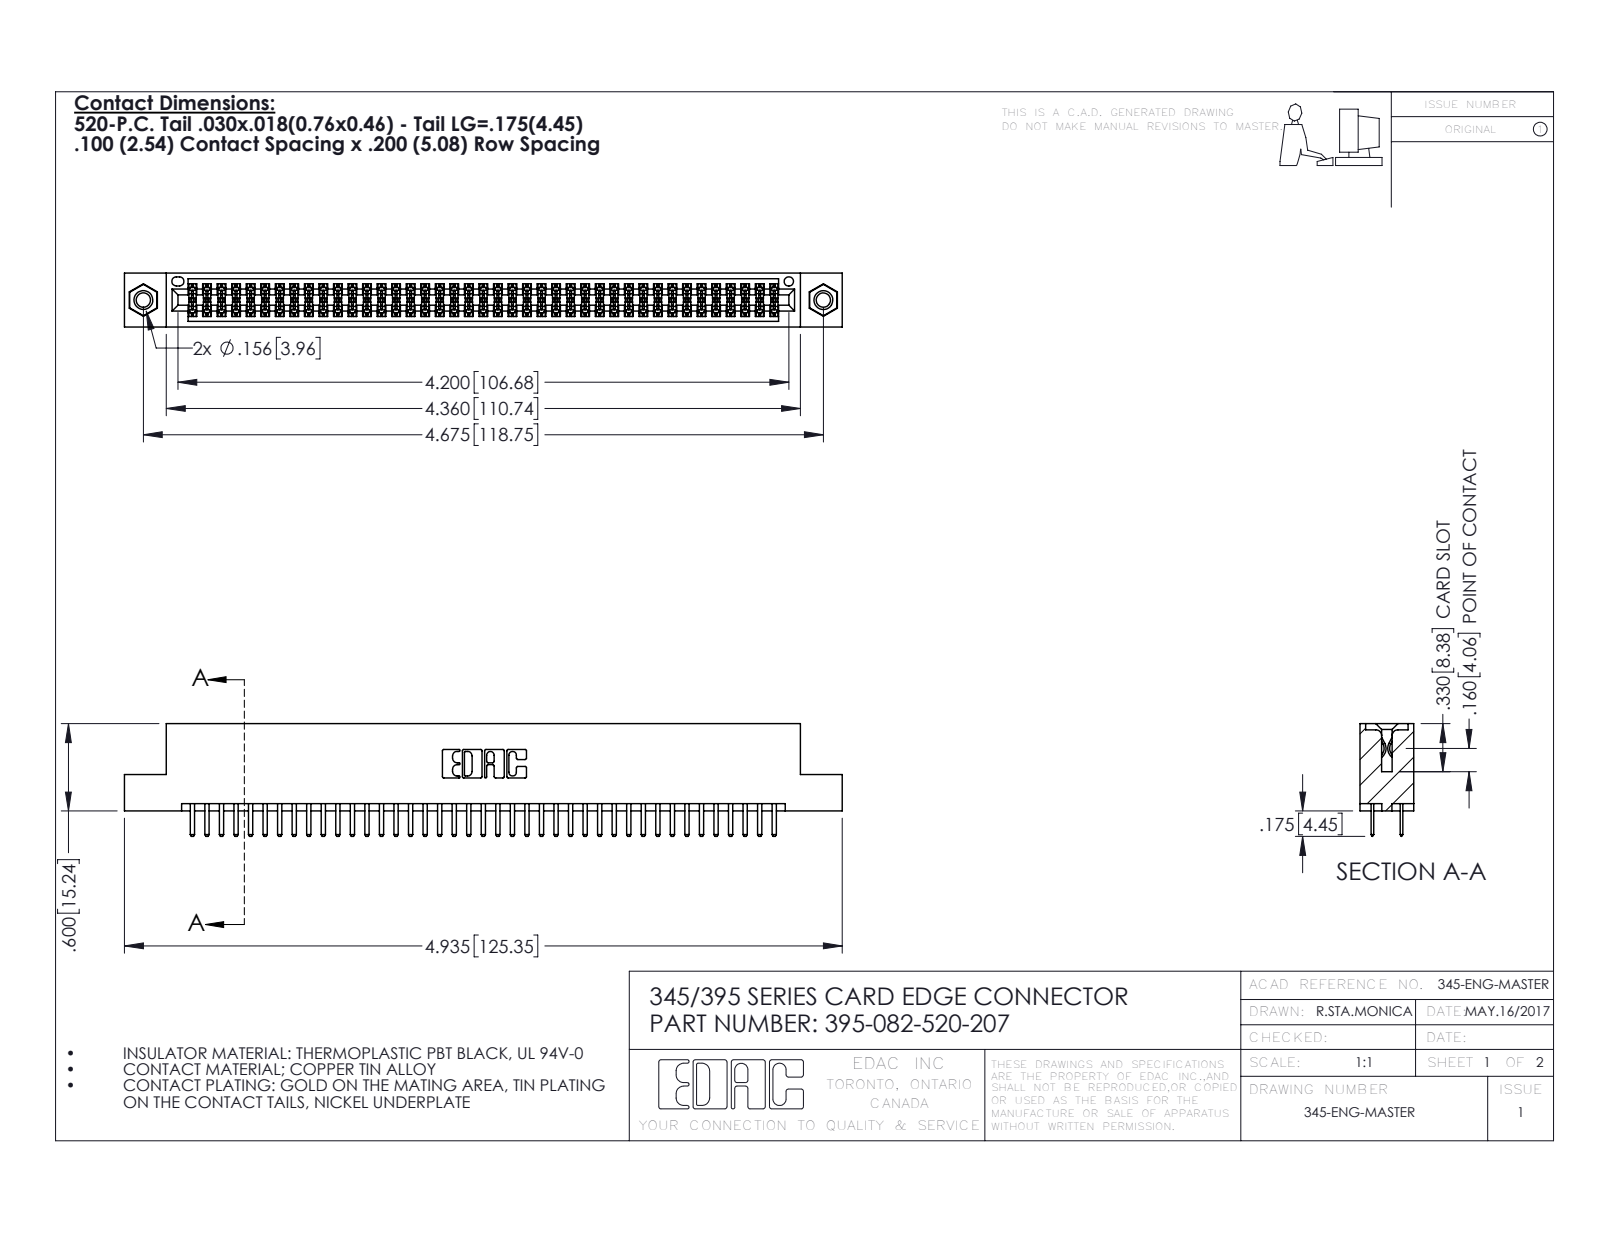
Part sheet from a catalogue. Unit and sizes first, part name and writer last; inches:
Units: inches
Overall size (bounding box): 4.935 × 0.775 × 0.37
Round holes (diameter × count): ⌀0.098 ×2, ⌀0.125 ×2, ⌀0.156 ×2, ⌀0.064 ×1
Round bosses / shafts (diameter × count): ⌀0.155 ×2
Partial cylindrical surfaces — rounded edges, fillets, slot ends (radius × count): R0.006 ×123, R0.01 ×86, R0.01 ×22, R0.007 ×6, R0.031 ×6, R0.026 ×3, R0.014 ×2, R0.019 ×2
Main face-to-face distances: 0.072, 0.298, 0.2, 0.37, 0.098, 0.272, 0.025, 0.225, 0.022, 0.072
Hole centre spacings: 0.27, 4.439, 4.675
Volume: 0.739 in³ · Surface area: 27.66 in²
Bodies: 85 solids, 4614 faces (2982 planar, 1616 cylindrical, 16 other)
Part name (STEP PRODUCT): 395-082-520-207; 345 Part_Flush Mounting Lugs - 0.156 Dia-TI; 345-292-001_345-293-120; 345-250-001_345-250-005-103
STEP written by: SolidWorks 2016 (CONFIG_CONTROL_DESIGN)
